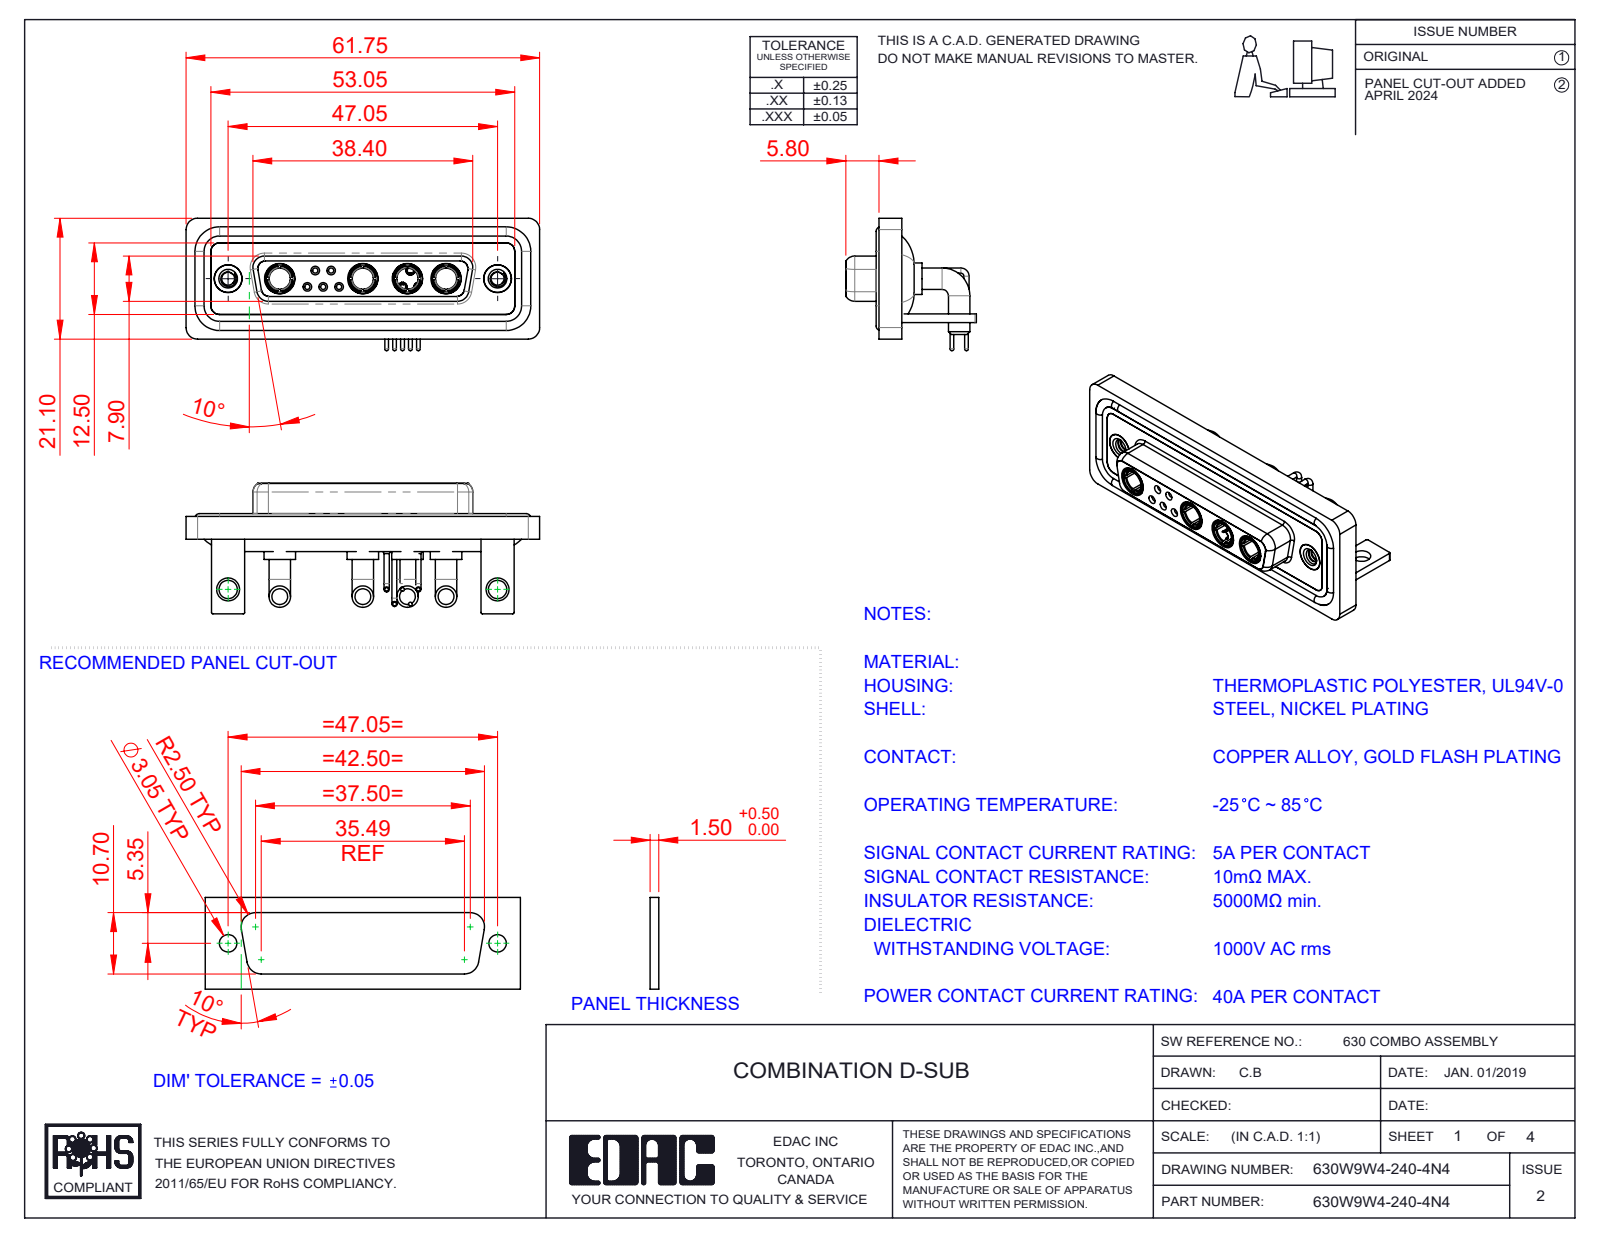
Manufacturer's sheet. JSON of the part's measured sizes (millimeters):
{"part_name": "630Combo Shell Rear_25 Contacts; 630Combo Contact Row 2_50 Contacts; 630Combo Stabilizer Bracket_50 Contacts; Power Socket_40A RA (+6 more)", "step_written_by": "SolidWorks 2023 (CONFIG_CONTROL_DESIGN)", "units": "millimeters", "bodies": {"solids": 22, "faces": 1011, "planar": 316, "cylindrical": 427, "other": 268}, "overall_size": [61.75, 23.12, 22.8], "volume_mm3": 9109, "surface_area_mm2": 14957, "round_holes": [[4.85, 6], [0.9, 5], [1.1, 5], [1.5, 5], [2, 5], [3.7, 4], [5.3, 4], [1.6, 3], [1.7, 2], [2.26, 2], [3.2, 2], [4, 2]], "round_bosses_or_shafts": [[0.9, 10], [1.6, 9], [3.75, 8], [2, 5], [1.5, 5], [0.65, 5], [5.5, 4], [5.2, 4]], "partial_cylinders_radius": [[2, 19], [1.5, 18], [0.25, 16], [1.35, 8], [1.6, 8], [0.5, 5], [0.6, 4], [0.65, 4]], "face_to_face_distances": [0.4, 1.8, 2.9, 3.7, 1.5, 4.1, 1.1, 1.4, 1.6, 2.5], "hole_center_spacings": [3.16, 2.77, 5.04, 13.85, 11.08, 12.79, 15.5, 5.54]}
